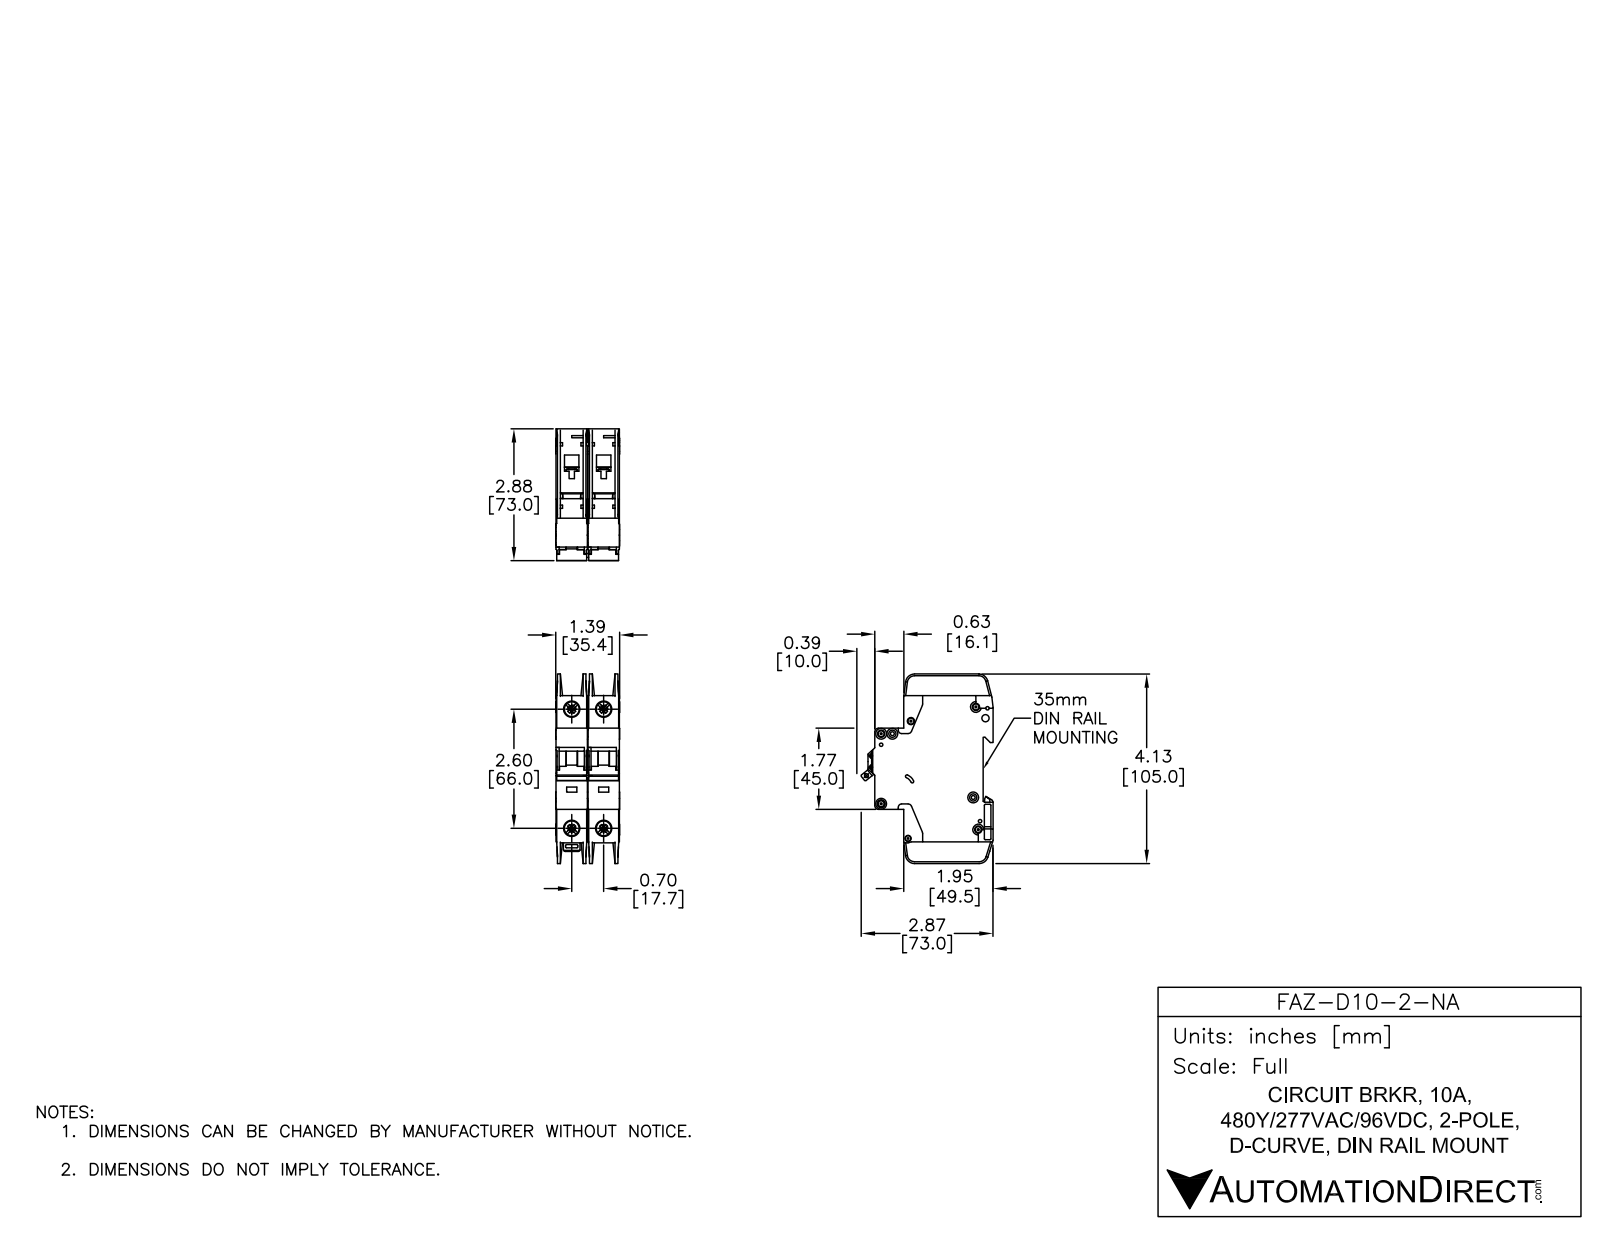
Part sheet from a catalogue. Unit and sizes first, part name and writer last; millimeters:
Units: millimetres
Overall size (bounding box): 105 × 73.04 × 35.4
Round holes (diameter × count): ⌀3.6 ×7, ⌀7.15 ×4, ⌀8.2 ×4, ⌀1.09 ×2, ⌀1.5 ×2, ⌀4 ×2, ⌀1.9 ×1, ⌀2.15 ×1, ⌀2.2 ×1, ⌀2.55 ×1, ⌀3.3 ×1, ⌀3.4 ×1
Round bosses / shafts (diameter × count): ⌀6 ×7, ⌀2.5 ×2
Partial cylindrical surfaces — rounded edges, fillets, slot ends (radius × count): R0.25 ×47, R0.5 ×24, R1 ×18, R2 ×12, R5 ×5, R1.8 ×4, R4 ×4, R0.2 ×2
Main face-to-face distances: 17.7, 17.5, 0.7, 15.05, 2.45, 1.75, 15.75, 13.3, 35.2, 17
Hole centre spacings: 6.2, 17.7, 66, 68.33, 5.19, 6.1, 8.19, 8.56
Volume: 155 390 mm³ · Surface area: 49 479 mm²
Bodies: 6 solids, 1568 faces (818 planar, 526 cylindrical, 224 other)
Part name (STEP PRODUCT): FAZ-D10-2-NA
STEP written by: SolidWorks 2014 (AUTOMOTIVE_DESIGN)
